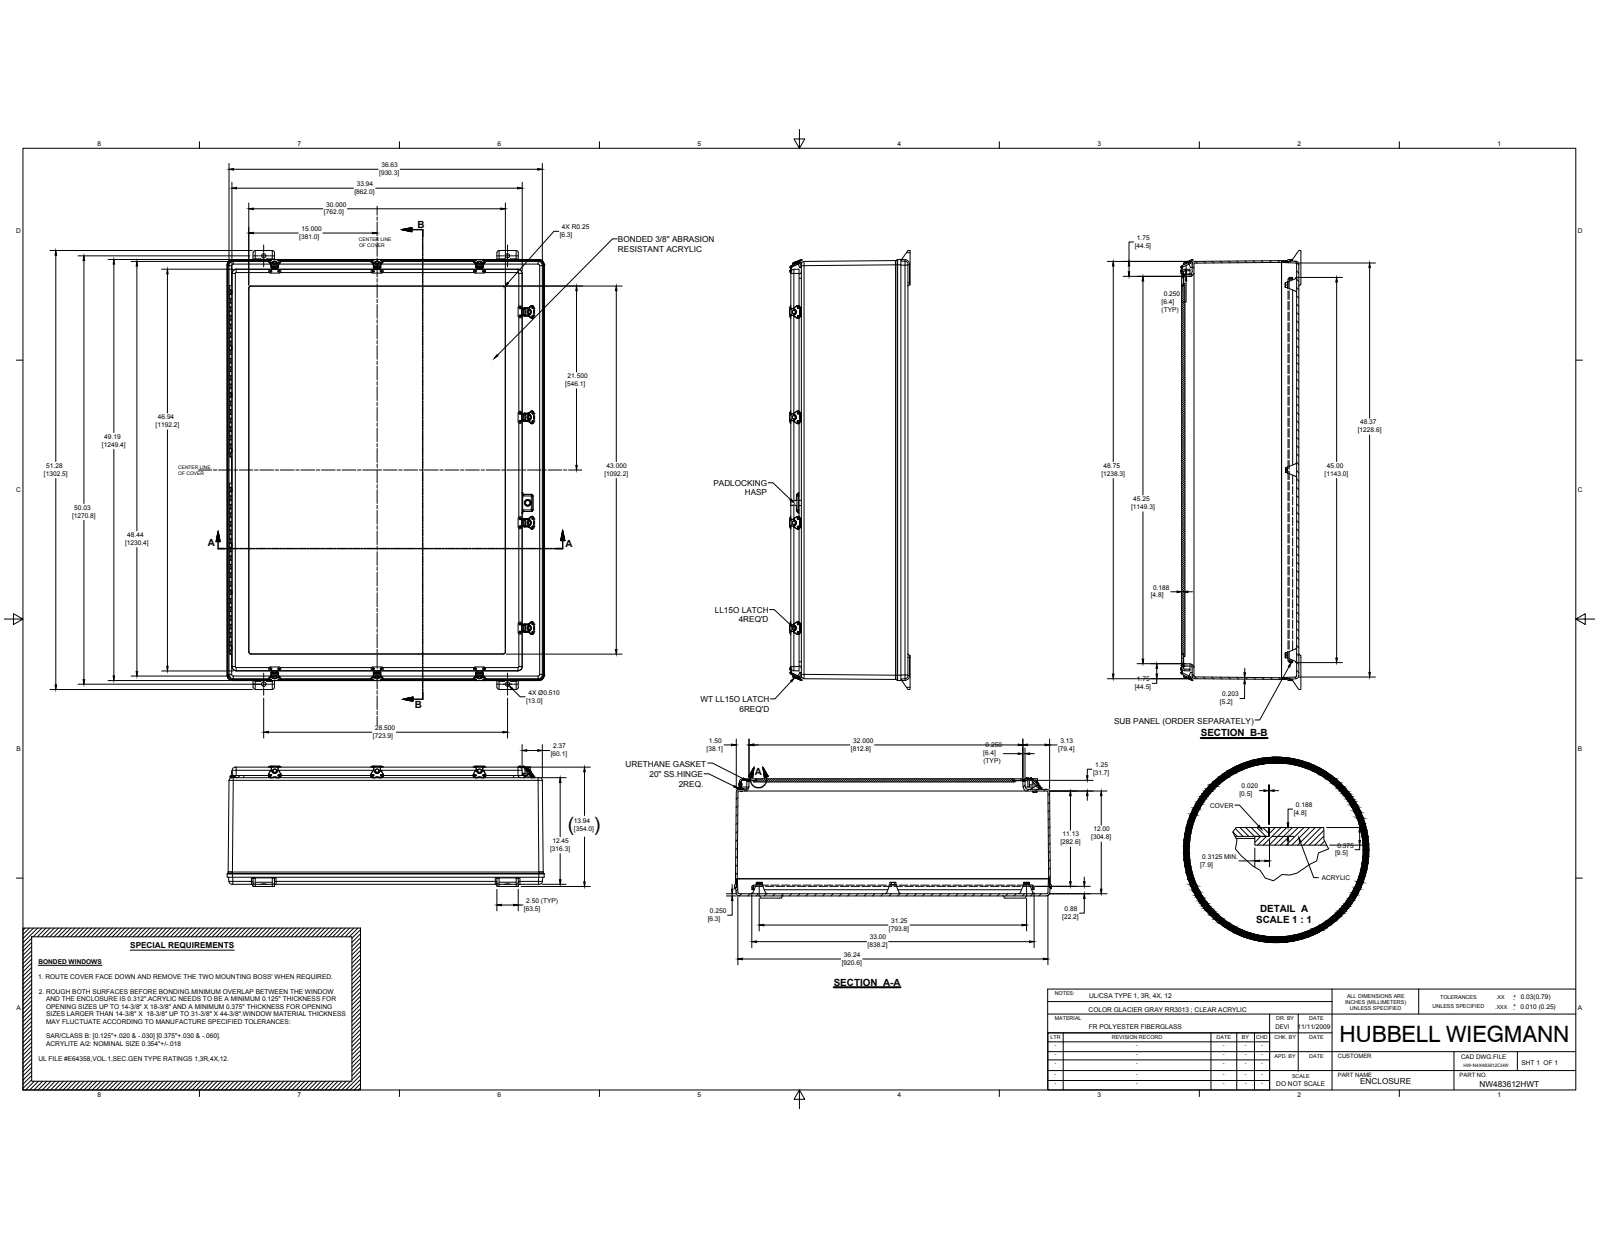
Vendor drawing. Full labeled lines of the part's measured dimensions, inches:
Part name (STEP PRODUCT): WPN4836B; WPN483612SHWT; SS HINGE COVER (20); 0.13 RIVET PIN (+8 more)
STEP written by: Autodesk Inventor 2014 (AUTOMOTIVE_DESIGN)
Units: inches
Bodies: 128 solids, 3151 faces (1193 planar, 1248 cylindrical, 710 other)
Overall size (bounding box): 51.281 × 37.063 × 14.072
Volume: 1 571 in³ · Surface area: 13 140 in²
Round holes (diameter × count): ⌀0.13 ×76, ⌀0.063 ×40, ⌀0.138 ×20, ⌀0.187 ×20, ⌀0.065 ×16, ⌀0.307 ×8, ⌀0.433 ×4, ⌀0.563 ×4, ⌀0.135 ×3, ⌀0.156 ×3, ⌀0.5 ×2, ⌀0.51 ×2
Round bosses / shafts (diameter × count): ⌀0.14 ×40, ⌀0.297 ×16, ⌀0.5 ×10, ⌀0.563 ×4, ⌀0.2 ×3, ⌀0.25 ×1, ⌀0.201 ×1
Partial cylindrical surfaces — rounded edges, fillets, slot ends (radius × count): R0.01 ×217, R0.03 ×40, R0.313 ×34, R0.25 ×28, R0.187 ×21, R0.21 ×20, R1.186 ×20, R0.375 ×18
Main face-to-face distances: 0.25, 13.677, 13.427, 13.302, 13.052, 0.375, 0.203, 0.203, 0.188, 0.187
Hole centre spacings: 6.5, 12, 1, 11.969, 12.313, 23.061, 5.5, 18.5
